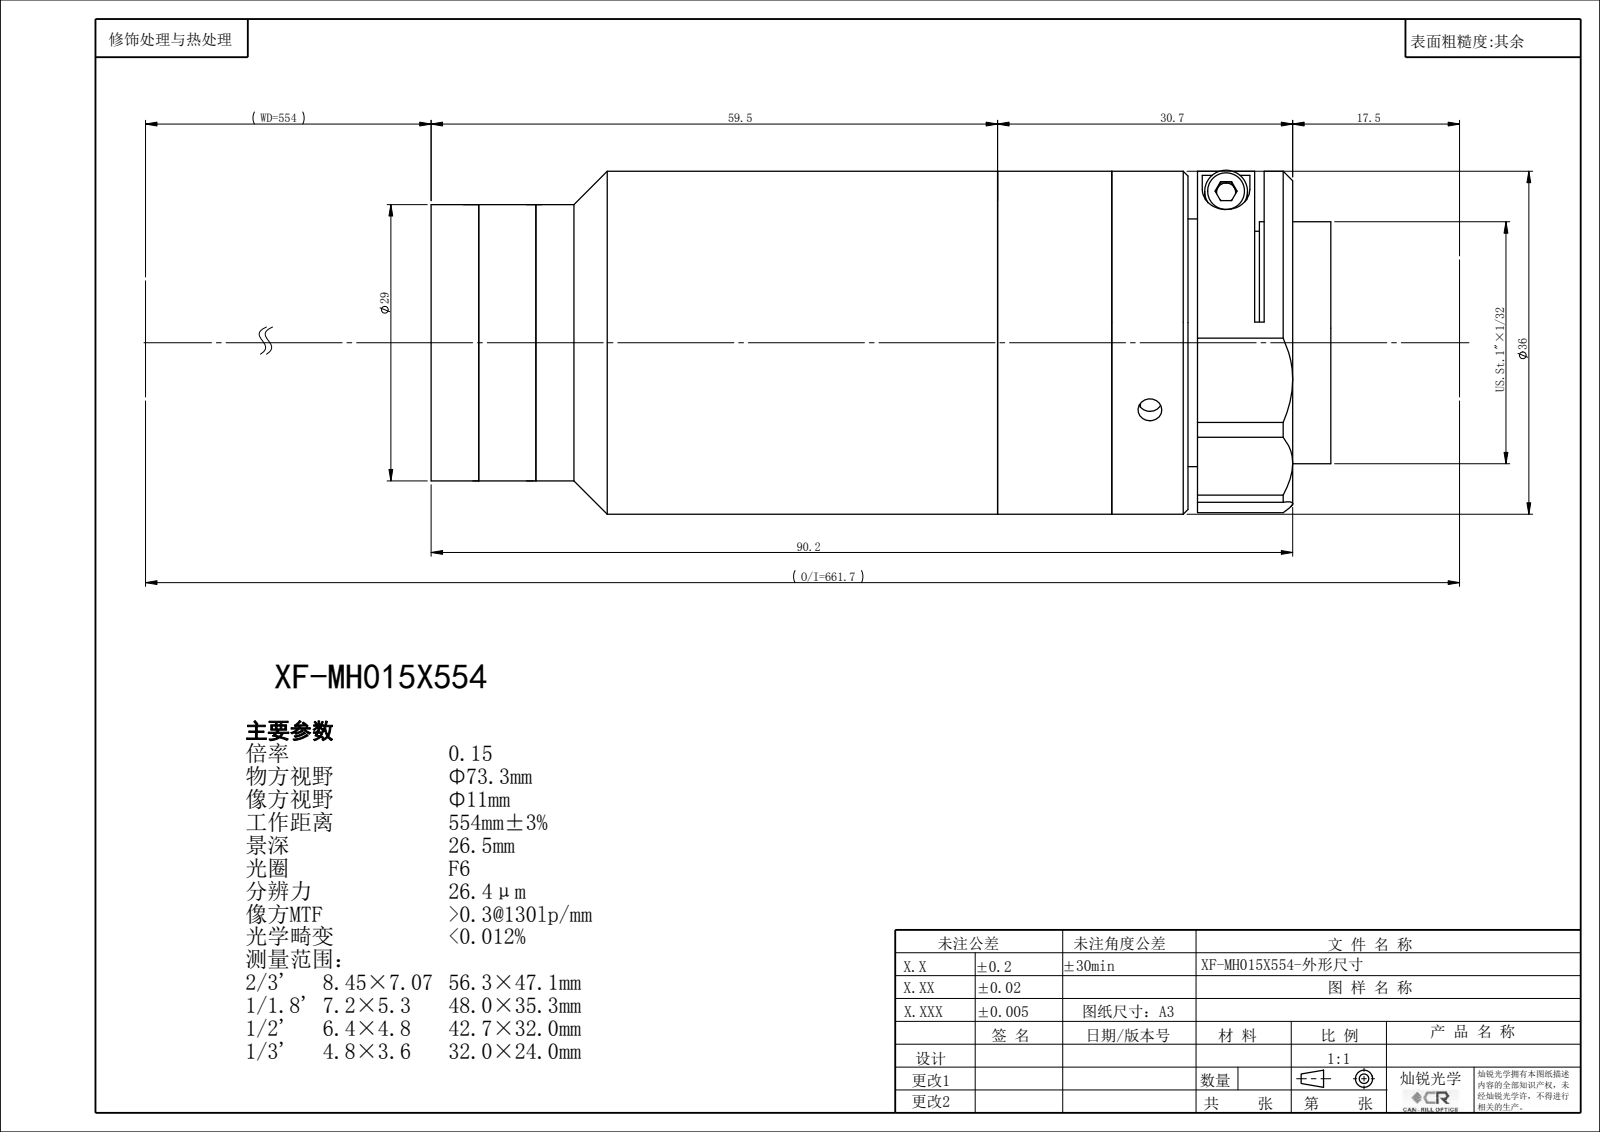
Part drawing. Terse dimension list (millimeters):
name: XF-MH015X554
written by: SolidWorks 2022 (CONFIG_CONTROL_DESIGN)
unit: mm
bodies: 0 solids, 124 faces (64 planar, 38 cylindrical, 22 other)
size: 94.21 × 36 × 36
holes: 3× ⌀2.5, 1× ⌀18, 1× ⌀22.4, 1× ⌀24, 1× ⌀24.9, 1× ⌀26.4
bosses: 1× ⌀36, 1× ⌀34, 1× ⌀29, 1× ⌀25.4
face distances: 1.5, 29.21, 30.71, 85.21, 18, 11.21, 12.71, 56, 74, 86.71
